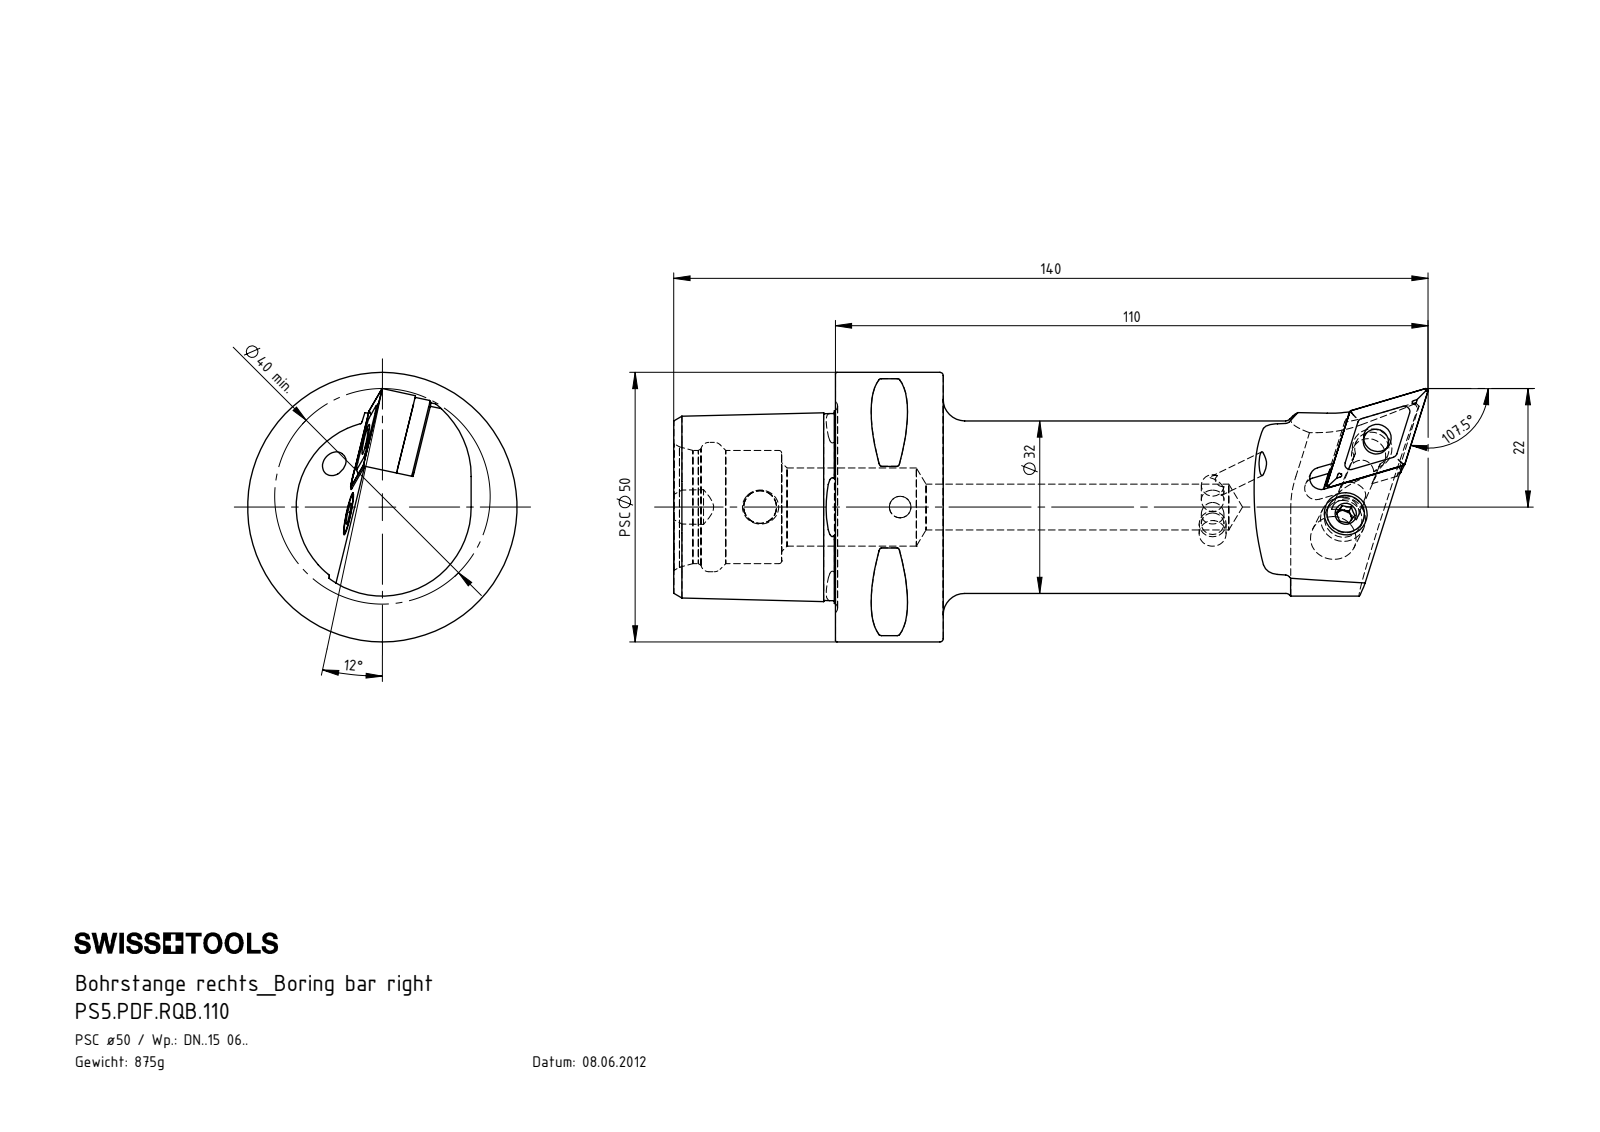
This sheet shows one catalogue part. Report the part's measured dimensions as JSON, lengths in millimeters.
{"part_name": "DNMG150604; WCD-ER1.101.000; WCD-ER4.101.017_A; KVT_MB_600_050 (+4 more)", "step_written_by": "SolidWorks 2017 (AUTOMOTIVE_DESIGN)", "units": "millimeters", "bodies": {"solids": 8, "faces": 350, "planar": 92, "cylindrical": 86, "other": 172}, "overall_size": [140, 50, 50], "volume_mm3": 112374, "surface_area_mm2": 26598, "round_holes": [[4, 3], [4.2, 1], [5.16, 1], [6.1, 1], [6.4, 1], [7, 1], [8.4, 1], [8.5, 1], [14.5, 1], [21, 1], [24, 1]], "round_bosses_or_shafts": [[50, 1], [32, 1], [8, 1], [7.9, 1], [6.4, 1], [5, 1], [4.7, 1], [3.55, 1]], "partial_cylinders_radius": [[0.5, 8], [0.4, 4], [1, 4], [2.5, 2], [2.1, 1], [2.35, 1], [2.8, 1], [3, 1]], "face_to_face_distances": [20, 30, 50, 6.05, 3.18, 9.23, 19.18, 12.28, 0.42, 12.7], "hole_center_spacings": [15.58, 26]}
